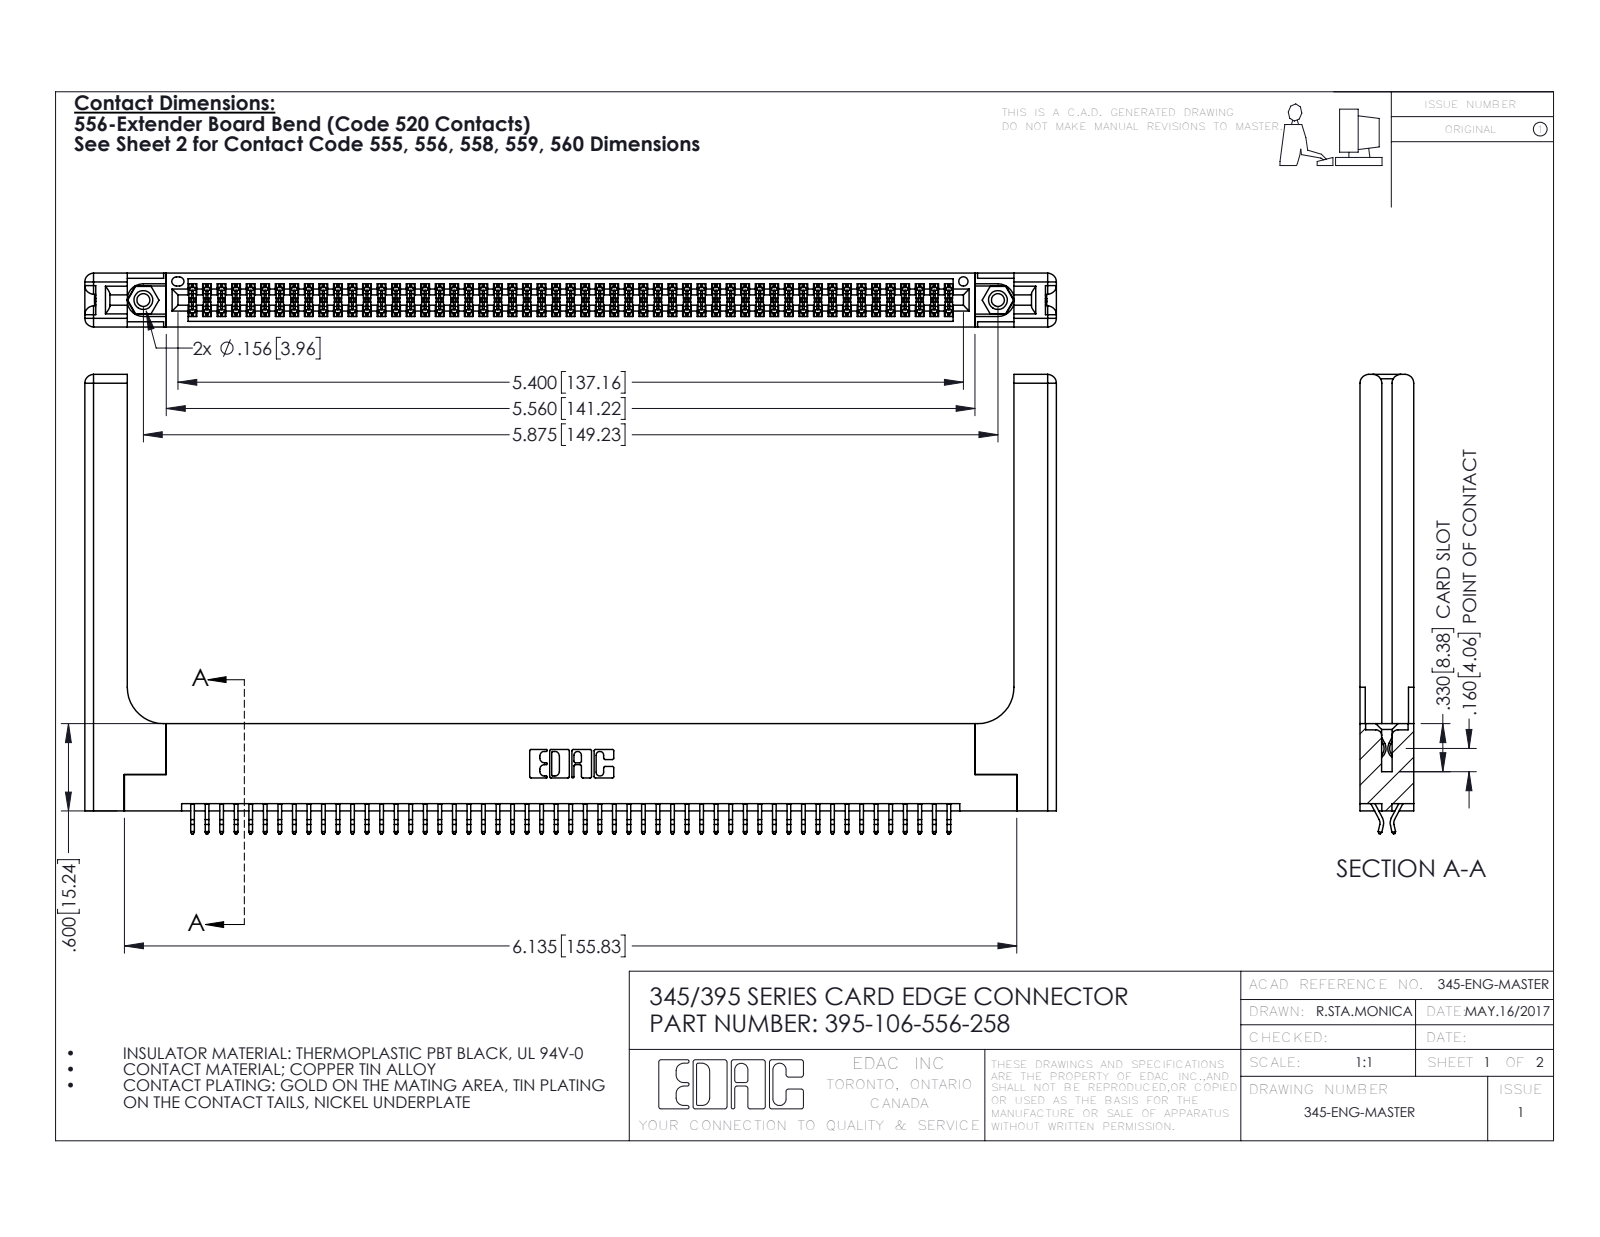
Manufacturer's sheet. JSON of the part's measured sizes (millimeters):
{"part_name": "345-250-001_345-250-001-102; 395-106-556-258; 345 Part_Flush Mounting Lugs - 0.156 Dia-TH; 345-292-001_556 Tail (+1 more)", "step_written_by": "SolidWorks 2016 (CONFIG_CONTROL_DESIGN)", "units": "millimeters", "bodies": {"solids": 111, "faces": 6318, "planar": 4150, "cylindrical": 2108, "other": 60}, "overall_size": [169.6, 80.2, 9.4], "volume_mm3": 25060, "surface_area_mm2": 29680, "round_holes": [[2.3, 2], [3.2, 2], [4, 2], [1.6, 1]], "round_bosses_or_shafts": [[3.9, 2]], "partial_cylinders_radius": [[0.2, 159], [0.3, 22], [1.5, 16], [0.2, 6], [0.8, 6], [0.7, 3], [0.3, 2], [0.4, 2]], "face_to_face_distances": [1.8, 7.6, 9.4, 5.1, 0.6, 2.5, 6.9, 5.7, 3.8, 3.8], "hole_center_spacings": [6.9, 143.2, 149.2]}
